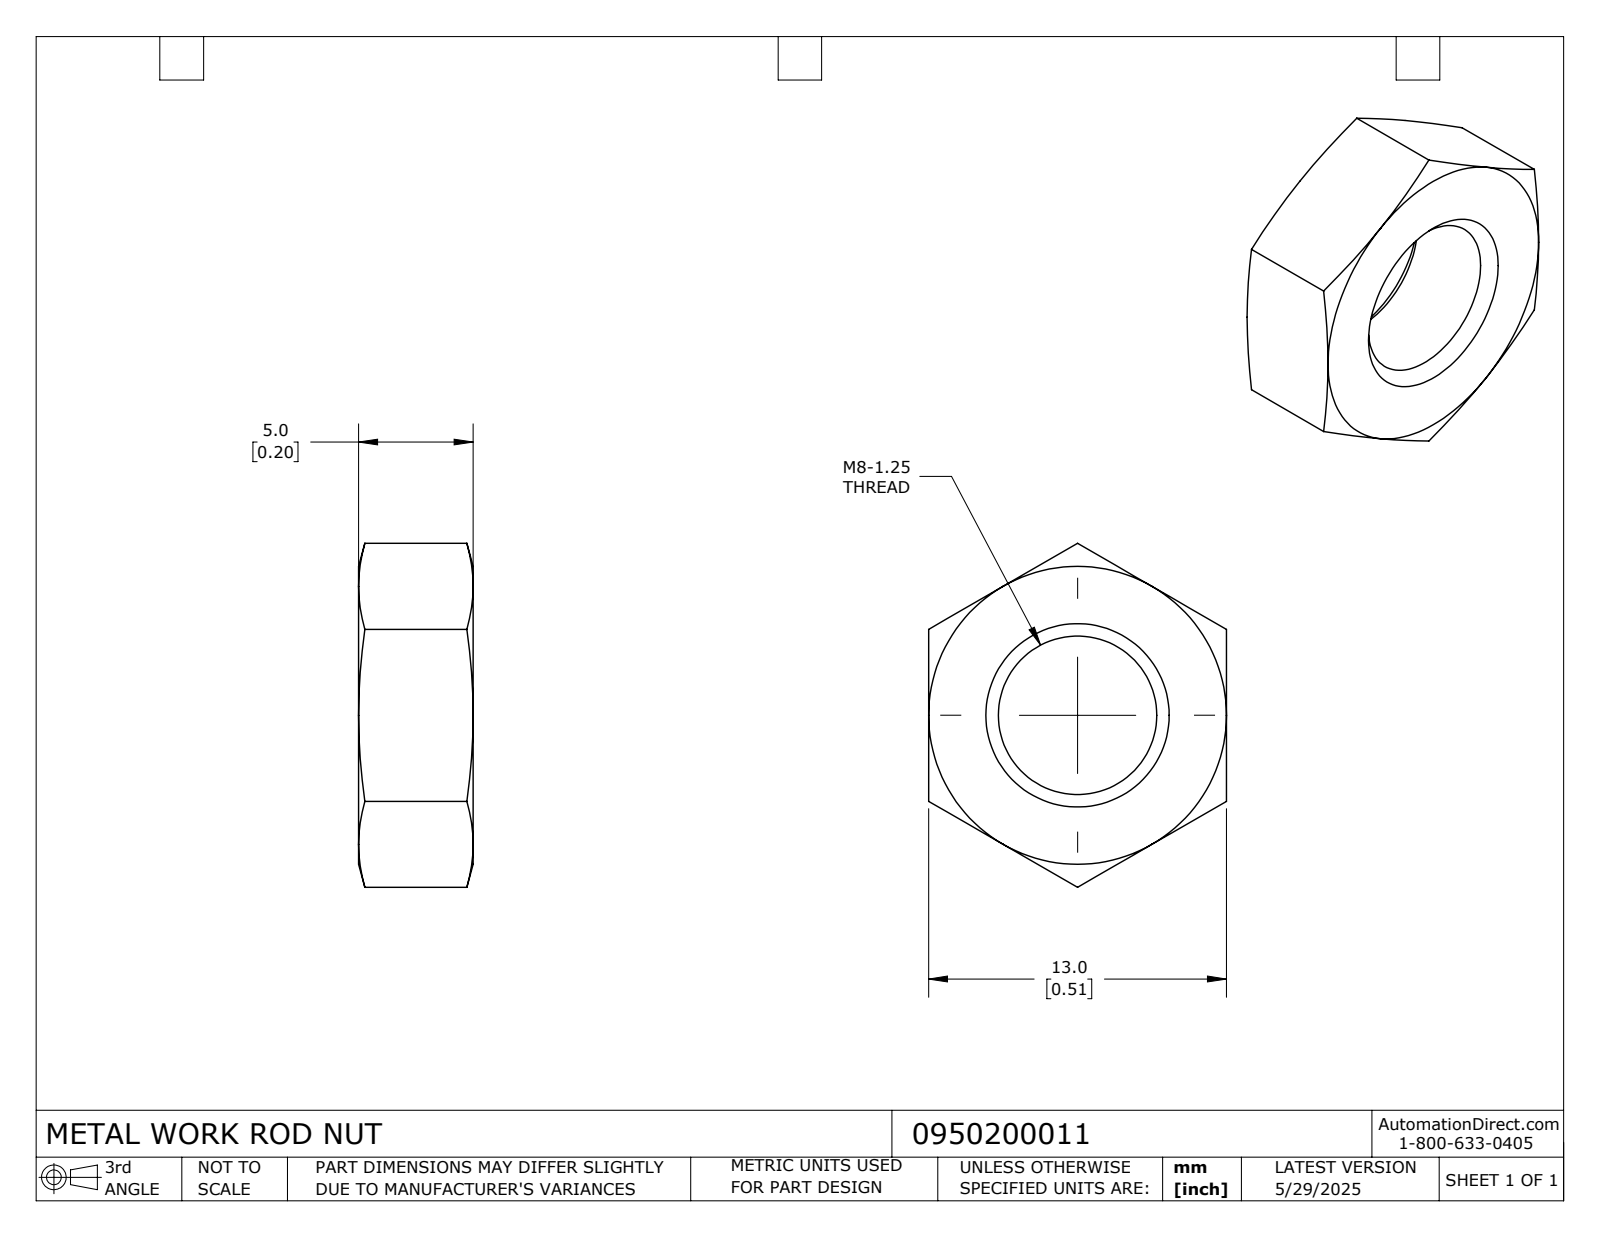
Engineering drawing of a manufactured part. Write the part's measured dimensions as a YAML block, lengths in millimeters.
part_name: "0950200011"
step_written_by: "SolidWorks 2024 (CONFIG_CONTROL_DESIGN)"
units: millimeters
bodies: {solids: 1, faces: 26, planar: 8, cylindrical: 2, other: 16}
overall_size: [15.01, 13, 5]
volume: 535
surface_area: 531
round_holes:
  - {diameter: 6.92, count: 1}
face_to_face_distances: [13, 5]
